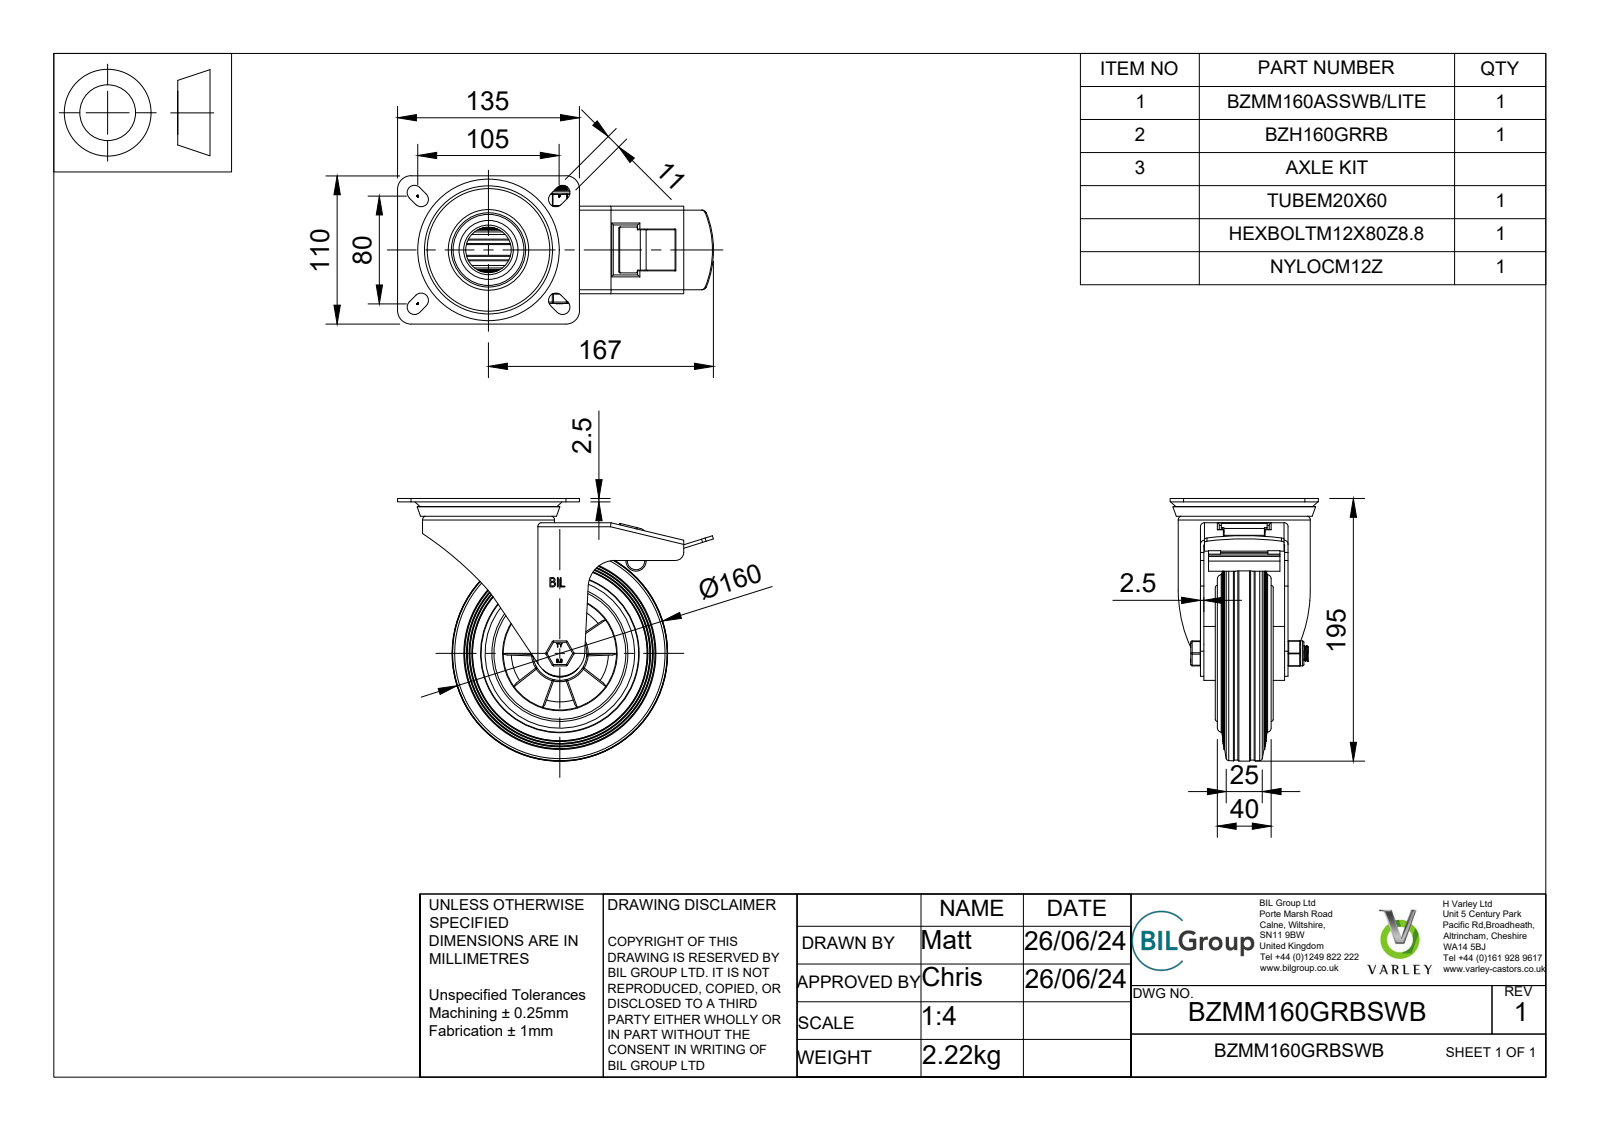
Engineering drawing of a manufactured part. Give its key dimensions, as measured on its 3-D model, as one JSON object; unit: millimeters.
{"part_name": "BZMM160GRBSWB v3; BZMM150ASSWBLITE v1; ZINC PLATED, PRESSED STEEL TOP PLATE; ZINC PLATED, PRESSED STEEL TOP PLATE Geometry (+7 more)", "step_written_by": "Autodesk Translation Framework v13.14.0.145 (AUTOMOTIVE_DESIGN)", "units": "millimeters", "bodies": {"solids": 61, "faces": 886, "planar": 315, "cylindrical": 204, "other": 367}, "overall_size": [234.5, 195, 110], "volume_mm3": 785093, "surface_area_mm2": 292079, "round_holes": [[10.2, 1], [12, 1], [12.5, 1], [14, 1], [20, 1], [33.75, 1], [34, 1], [35, 1], [39.75, 1], [72, 1], [85, 1], [93, 1]], "round_bosses_or_shafts": [[7.5, 8], [158.4, 1], [101, 1], [98, 1], [78, 1], [50, 1], [40, 1], [34.9, 1]], "partial_cylinders_radius": [[0.5, 19], [1, 13], [1.5, 12], [5.5, 8], [3, 7], [0.75, 6], [2, 4], [10, 4]], "face_to_face_distances": [2.5, 9, 5, 1, 62.5, 18, 4, 60, 3, 13]}
